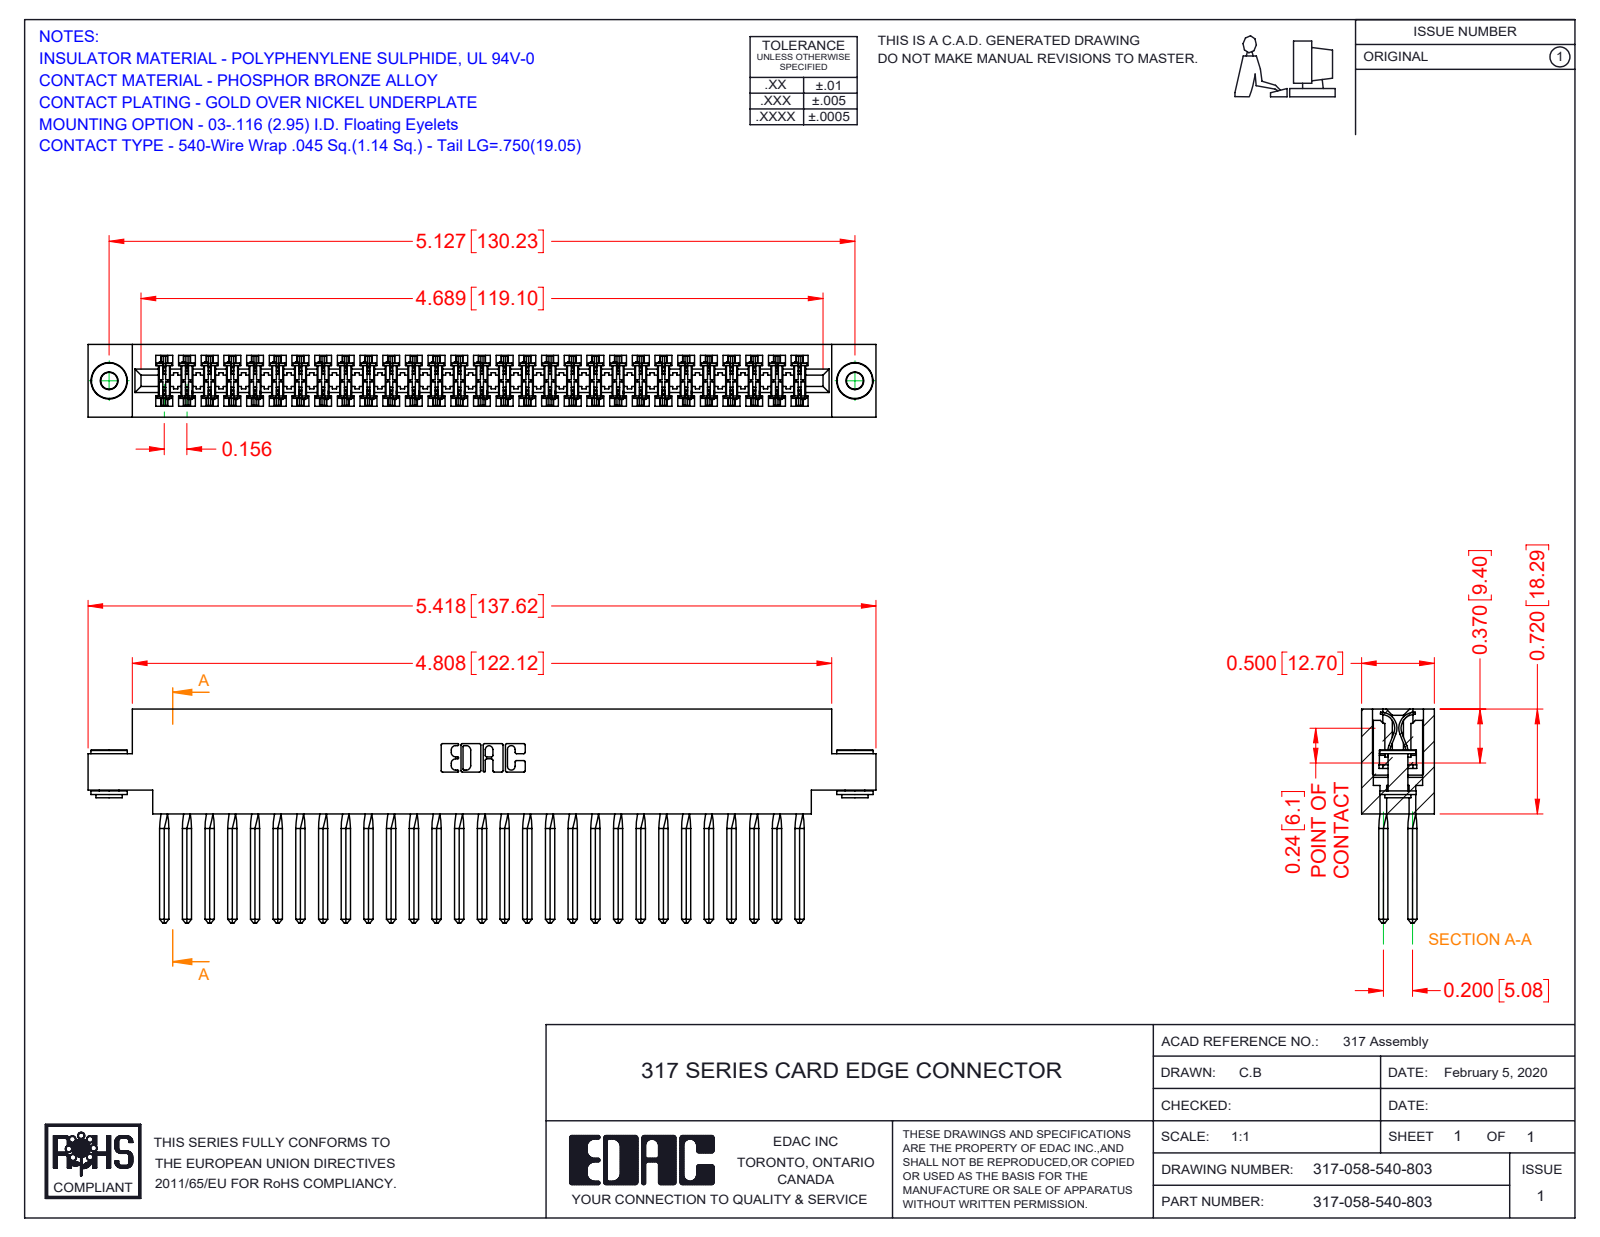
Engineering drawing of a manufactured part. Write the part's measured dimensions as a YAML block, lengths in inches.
part_name: "317-058-540-803; 317 Part_.156 Dia - TH; 345-250-002_345-250-002-102; 317-290-001_540"
step_written_by: "SolidWorks 2016 (CONFIG_CONTROL_DESIGN)"
units: inches
bodies: {solids: 61, faces: 5302, planar: 4302, cylindrical: 760, other: 240}
overall_size: [5.418, 1.47, 0.5]
volume: 1.384
surface_area: 51.97
round_holes:
  - {diameter: 0.116, count: 2}
  - {diameter: 0.156, count: 2}
round_bosses_or_shafts:
  - {diameter: 0.25, count: 2}
  - {diameter: 0.18, count: 2}
  - {diameter: 0.136, count: 2}
partial_cylinders:
  - {radius: 0.015, count: 116}
  - {radius: 0.01, count: 22}
  - {radius: 0.007, count: 6}
  - {radius: 0.031, count: 6}
  - {radius: 0.026, count: 3}
  - {radius: 0.095, count: 2}
  - {radius: 0.1, count: 2}
  - {radius: 0.11, count: 2}
face_to_face_distances: [0.5, 0.075, 0.425, 0.35, 0.11, 0.195, 0.094, 0.2, 0.72, 0.115]
hole_center_spacings: [5.127]
